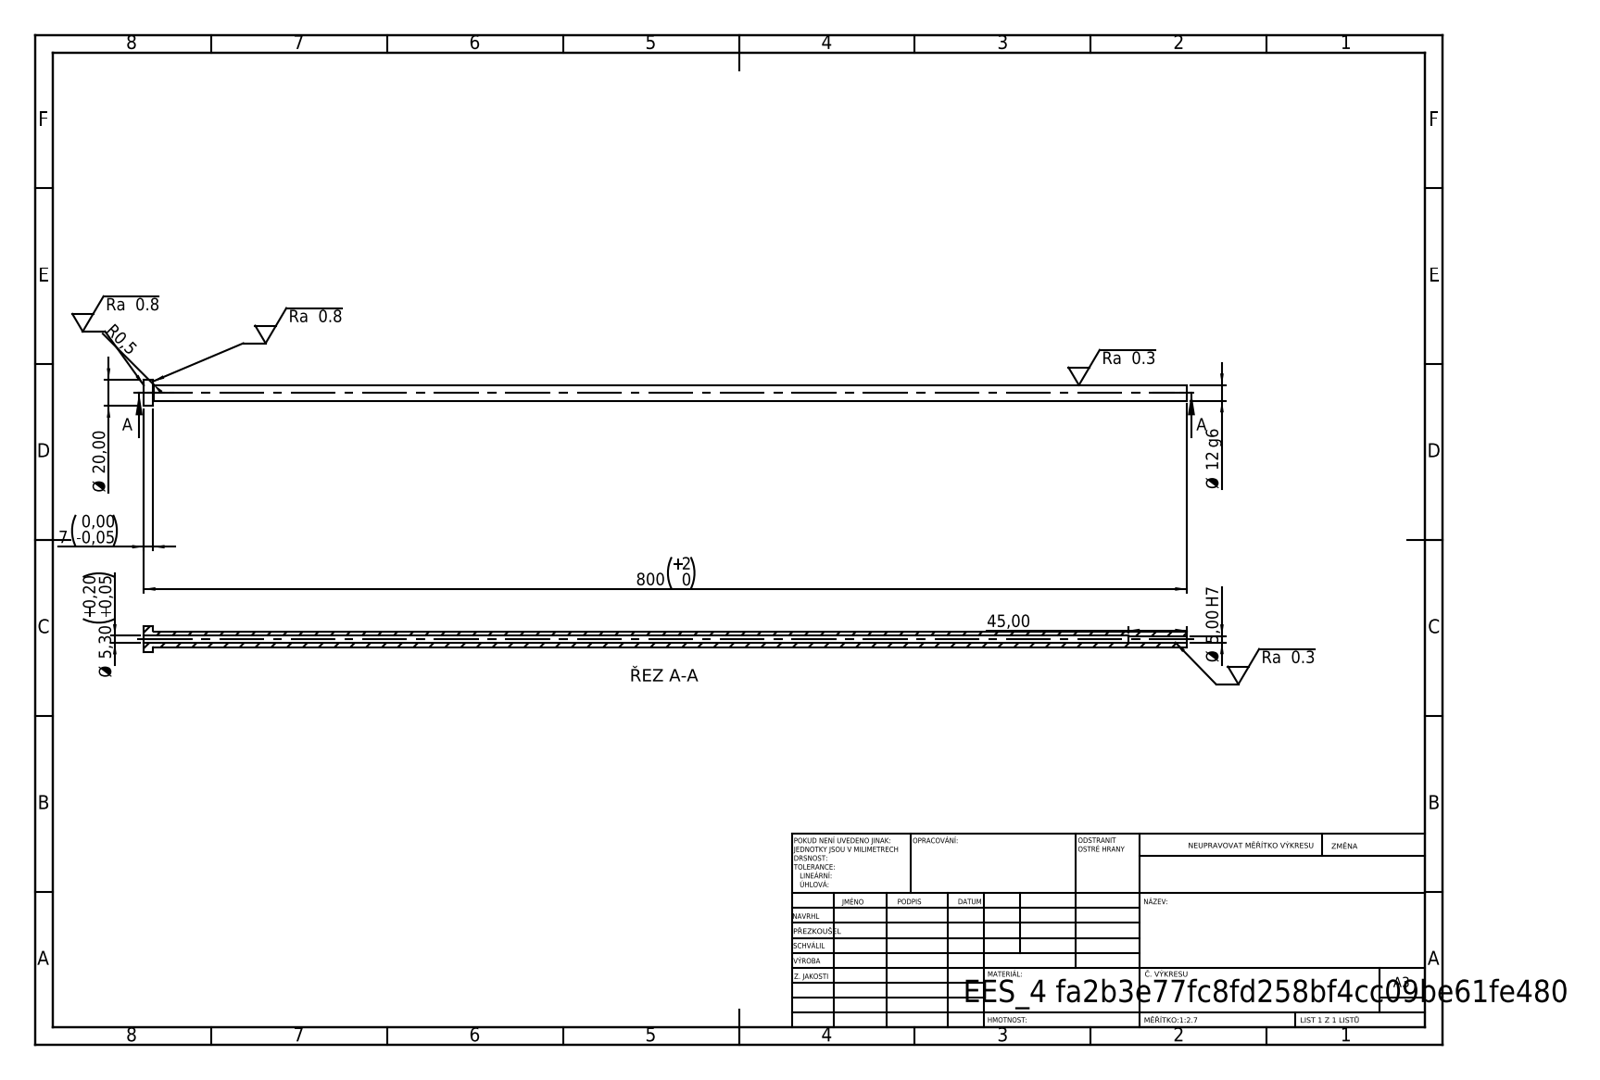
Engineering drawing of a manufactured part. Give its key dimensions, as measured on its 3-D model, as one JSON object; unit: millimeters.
{"step_written_by": "SolidWorks 2019 (CONFIG_CONTROL_DESIGN)", "units": "millimeters", "bodies": {"solids": 1, "faces": 14, "planar": 4, "cylindrical": 8, "other": 2}, "overall_size": [800, 20, 20], "volume_mm3": 74347, "surface_area_mm2": 44194, "round_holes": [[5, 1], [5.3, 1]], "round_bosses_or_shafts": [[20, 1], [12, 1]], "face_to_face_distances": [7, 800, 793, 755, 748, 45]}
